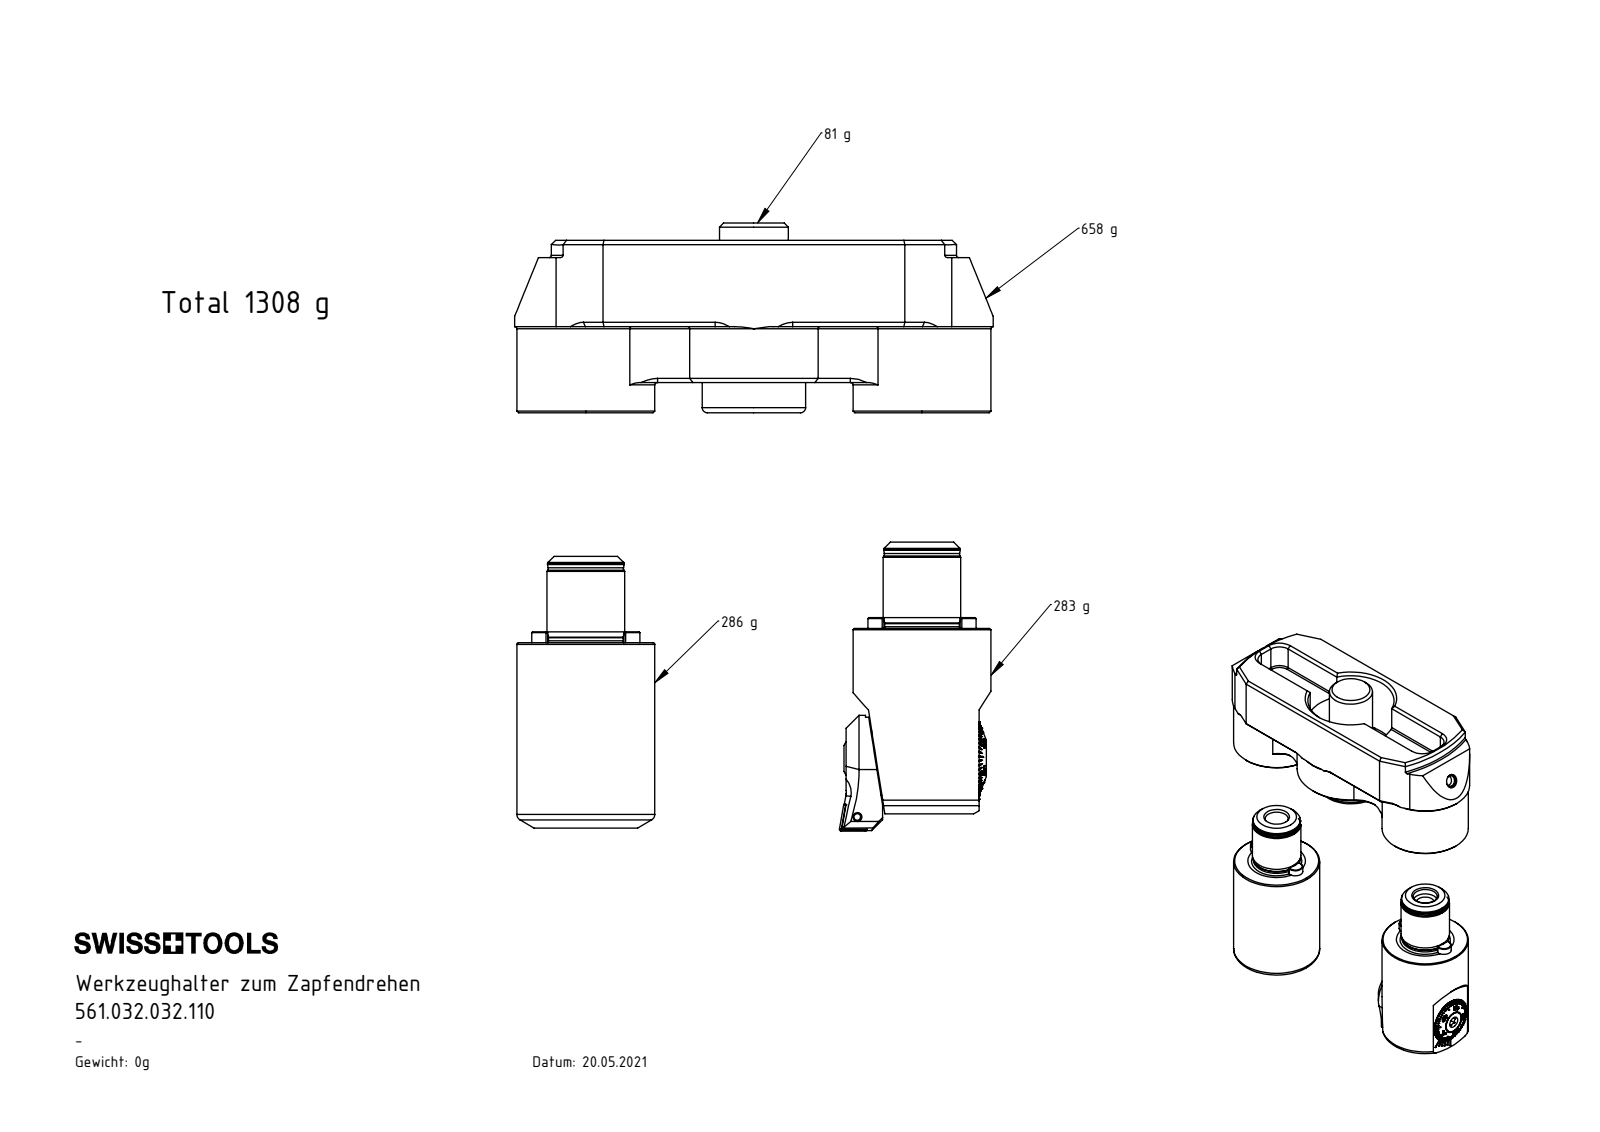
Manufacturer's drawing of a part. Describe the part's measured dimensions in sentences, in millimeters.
The part is named "ISO 4026 - M6 x 5_PreviewCfg; F32-WCA.001.007_C_fertigbearbeitet; F32-BG3.006.026_A; F32-ER1.101.010_A (+8 more)". Its 3-D file was written by "SolidWorks 2017 (CONFIG_CONTROL_DESIGN)". It is 34 solids with 1706 faces: 552 planar, 403 cylindrical and 751 other. Overall it measures 178.9 by 111 by 72 millimeters. Its volume is 365 402 cubic millimeters and its surface area 97 457 square millimeters. Round holes: 11 of diameter 5, 5 of diameter 2.5, 5 of diameter 2.8, 3 of diameter 3, 3 of diameter 19, 2 of diameter 2, 2 of diameter 4, 2 of diameter 4.2, 2 of diameter 5.25, 2 of diameter 8, 2 of diameter 8.5, 2 of diameter 12. Round bosses or shafts: 6 of diameter 6, 2 of diameter 32, 2 of diameter 17.8, 2 of diameter 17.3, 2 of diameter 14, 2 of diameter 5, 2 of diameter 4.6, 2 of diameter 2.5. Partial cylindrical surfaces (rounded edges, fillets, slot ends): 16 of radius 0.5, 6 of radius 0.21, 6 of radius 1.4, 5 of radius 0.36, 4 of radius 2.5, 4 of radius 2.73, 4 of radius 2.88, 4 of radius 4.5. The main face-to-face distances are 40, 13, 7, 16, 20, 14, 10, 18, 58, 42. The hole center spacings are 78, 10.85, 1.15, 12, 12.25, 13.48, 17.05, 20.28.
